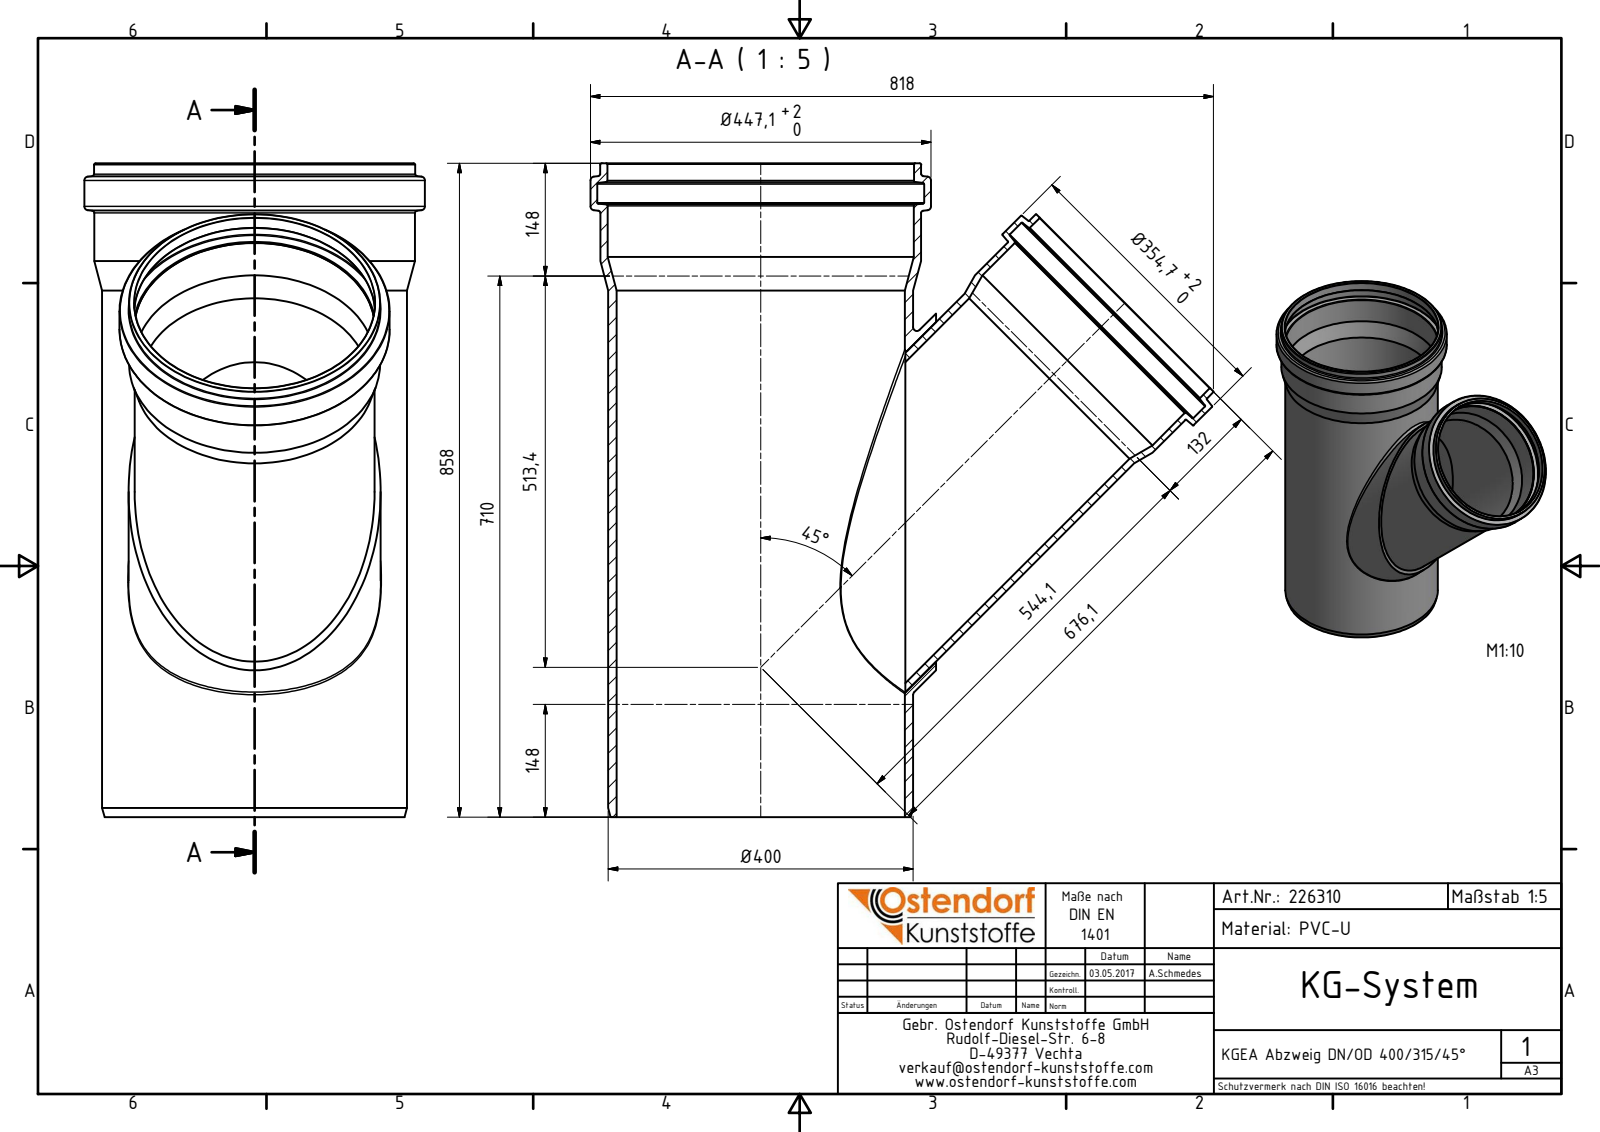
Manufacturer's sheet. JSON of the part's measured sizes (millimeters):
{"part_name": "226310 KGEA Abzweig DN_OD 400_315_45°; 226310 KGEA Abzweig DN_OD 400_315_45° Abzweig", "step_written_by": "Autodesk Inventor 2016 (AUTOMOTIVE_DESIGN)", "units": "millimeters", "bodies": {"solids": 2, "faces": 60, "planar": 6, "cylindrical": 19, "other": 35}, "overall_size": [858, 818, 447.1], "volume_mm3": 14560000, "surface_area_mm2": 3034000, "round_holes": [[315.9, 2], [297.6, 1], [315, 1], [315.6, 1], [340.9, 1], [378.35, 1], [402, 1], [402.4, 1], [429.1, 1]], "round_bosses_or_shafts": [[447.1, 1], [421.4, 1], [421.1, 1], [400.35, 1], [354.7, 1], [331, 1], [329.7, 1], [329.4, 1]], "face_to_face_distances": [40.24, 858, 46.55]}
